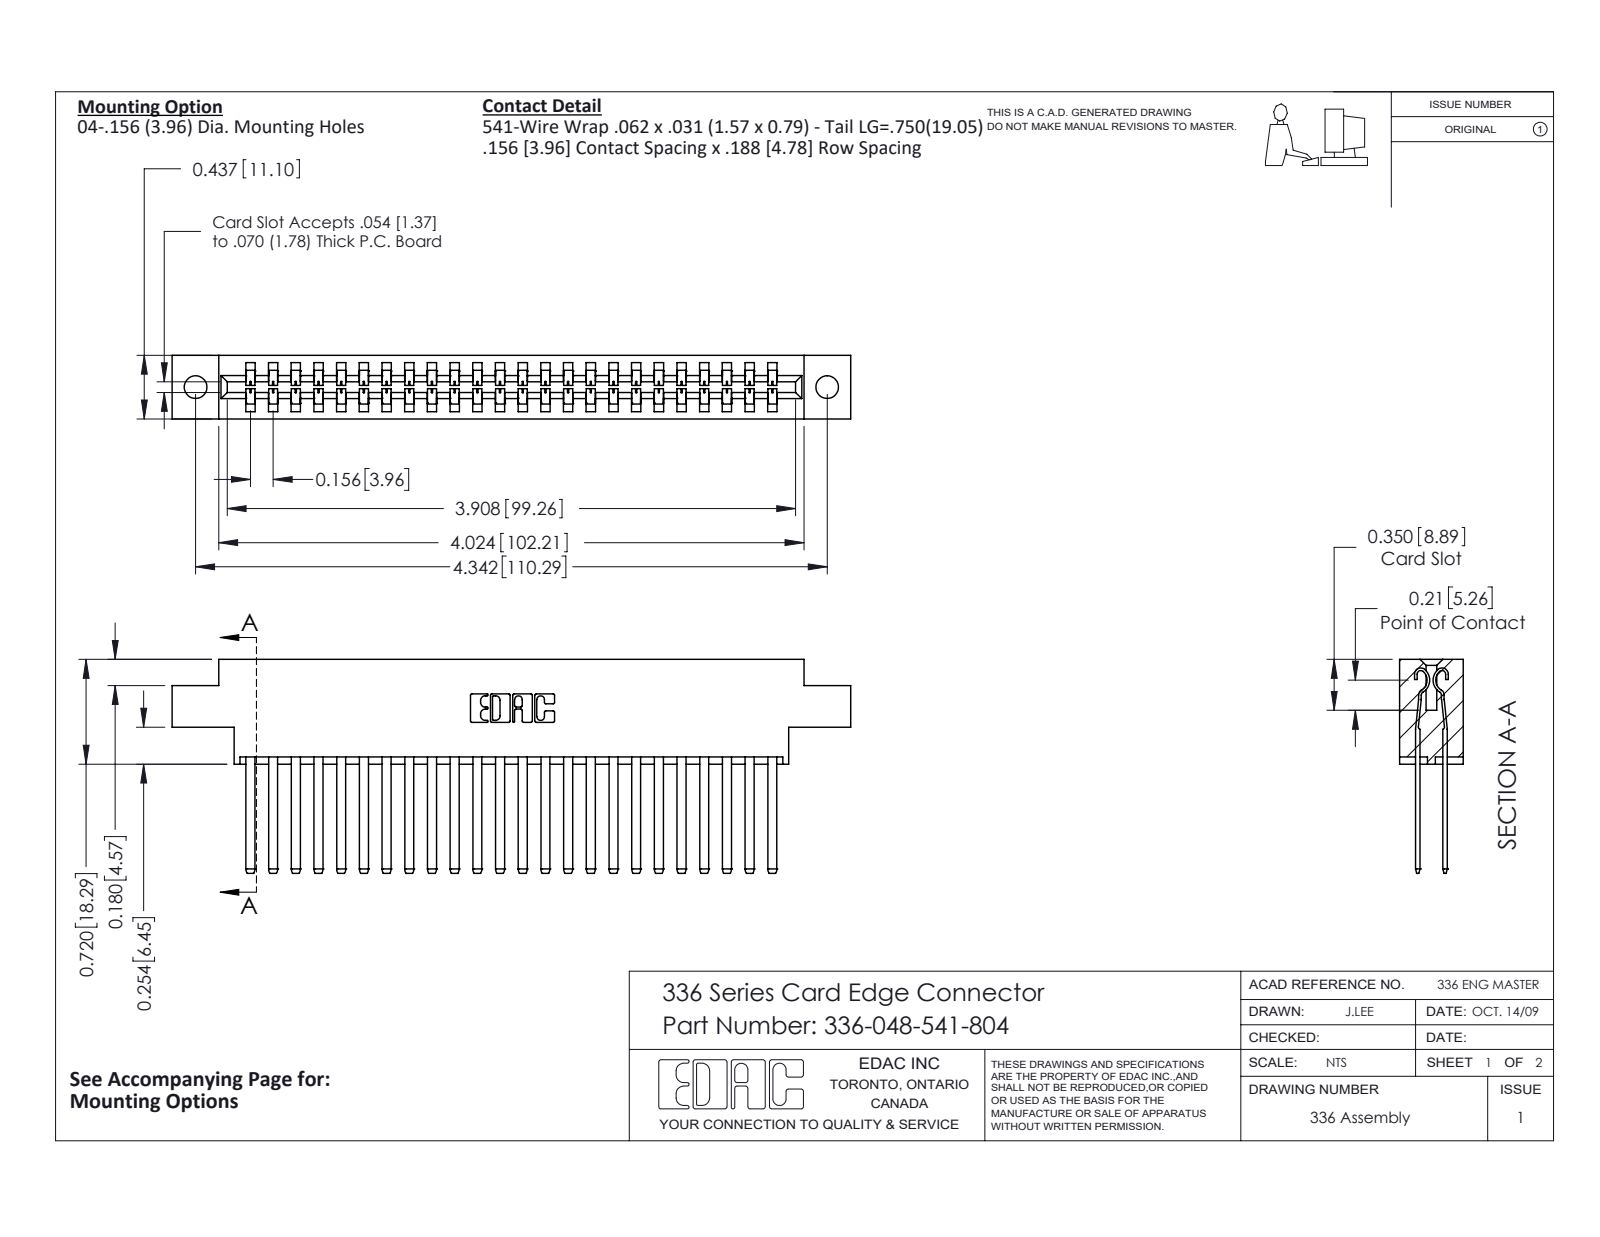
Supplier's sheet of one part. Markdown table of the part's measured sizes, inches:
| quantity | value |
| --- | --- |
| part name | 336-290-001_336-290-541; 336 Part_Offset - .156 Dia - TH; 336-048-541-804 |
| STEP written by | SolidWorks 2020 (CONFIG_CONTROL_DESIGN) |
| units | inches |
| bodies | 49 solids, 2134 faces (1322 planar, 812 cylindrical, 0 other) |
| overall size | 4.665 × 1.47 × 0.437 |
| volume | 1.076 in³ |
| surface area | 34.22 in² |
| round holes (diameter × count) | 0.156 × 2 |
| partial cylindrical surfaces (radius × count) | 0.004 × 96, 0.056 × 48, 0.01 × 22, 0.007 × 6, 0.031 × 6, 0.022 × 4, 0.04 × 4, 0.026 × 3 |
| main face-to-face distances | 0.188, 0.328, 0.14, 0.297, 0.109, 0.031, 0.437, 0.033, 0.181, 0.156 |
| hole center spacings | 4.342 |
